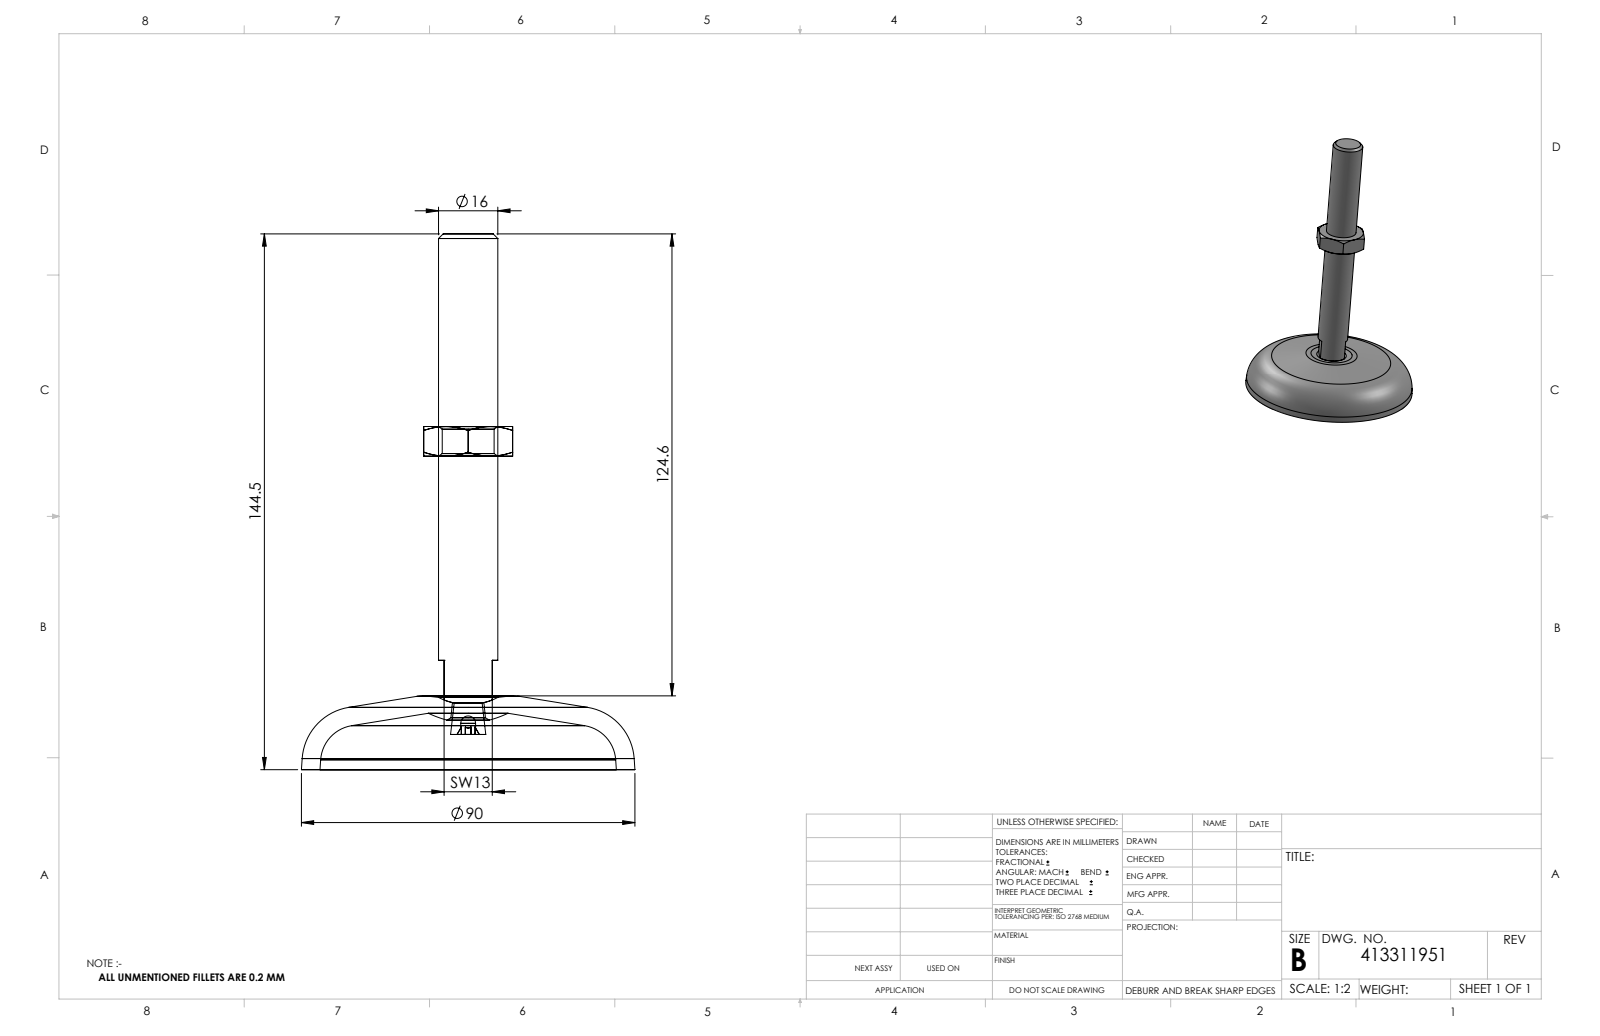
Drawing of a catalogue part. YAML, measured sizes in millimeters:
part_name: "413311951_c_1"
step_written_by: "SolidWorks 2014 (CONFIG_CONTROL_DESIGN)"
units: millimeters
bodies: {solids: 3, faces: 85, planar: 27, cylindrical: 8, other: 50}
overall_size: [144.5, 90, 90]
volume: 68083
surface_area: 26079
round_holes:
  - {diameter: 4, count: 1}
  - {diameter: 14, count: 1}
  - {diameter: 16, count: 1}
face_to_face_distances: [24, 84.56, 92.56, 8, 5.5, 18.5, 144.5, 59.94, 51.94, 13]
